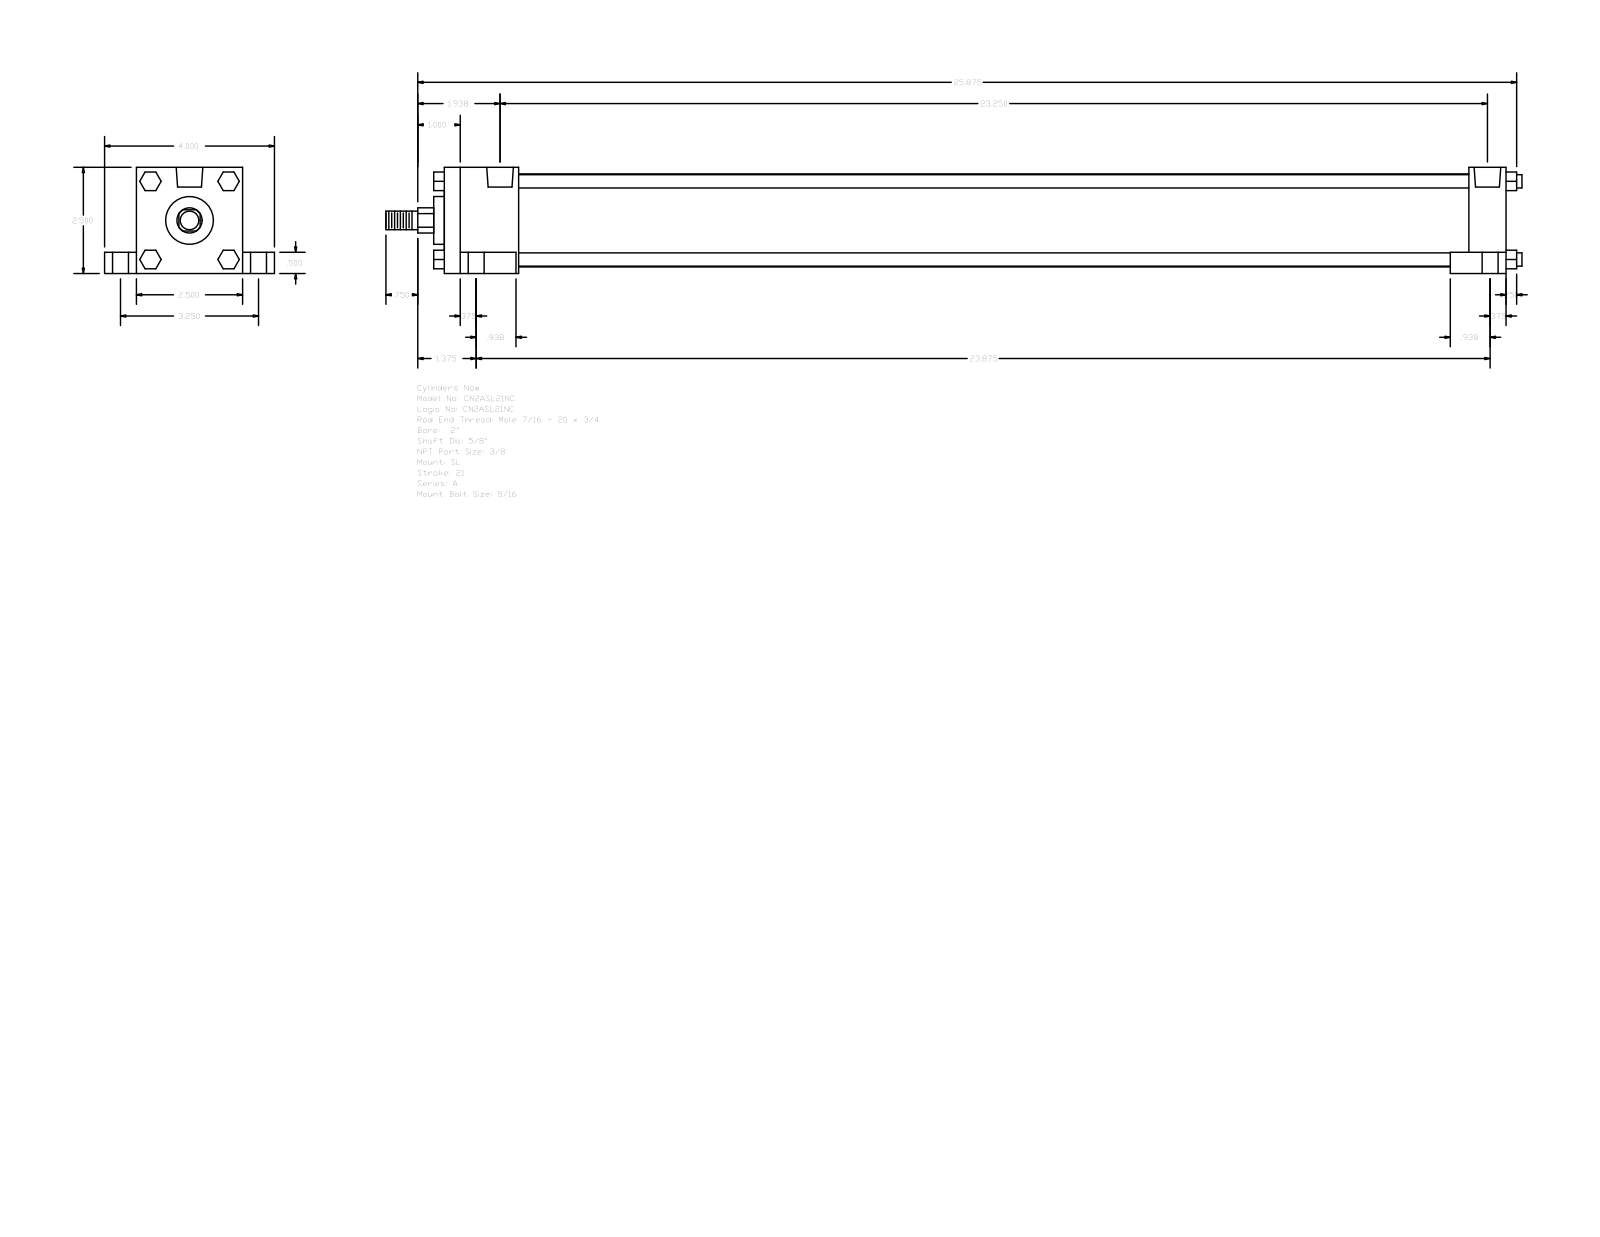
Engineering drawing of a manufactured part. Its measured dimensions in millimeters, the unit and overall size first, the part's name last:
Units: millimetres
Overall size (bounding box): 679.45 × 101.6 × 63.5
Round holes (diameter × count): ⌀5.56 ×4, ⌀9.53 ×4, ⌀15.88 ×4, ⌀15.93 ×2
Round bosses / shafts (diameter × count): ⌀7.94 ×4, ⌀55.63 ×1, ⌀28.57 ×1, ⌀15.88 ×1, ⌀11.11 ×1
Partial cylindrical surfaces — rounded edges, fillets, slot ends (radius × count): R7.54 ×1
Main face-to-face distances: 63.5, 635, 50.8, 12.7, 19.05, 82.55, 44.45, 590.55, 612.77, 568.32
Hole centre spacings: 41.3, 41.64, 43.67, 45.13, 82.54, 582.6, 589.61, 593.58
Bodies: 0 solids, 148 faces (112 planar, 36 cylindrical, 0 other)
Part name (STEP PRODUCT): A_SL__0200_0.625
STEP written by: GSSL Pune (CONFIG_CONTROL_DESIGN)
